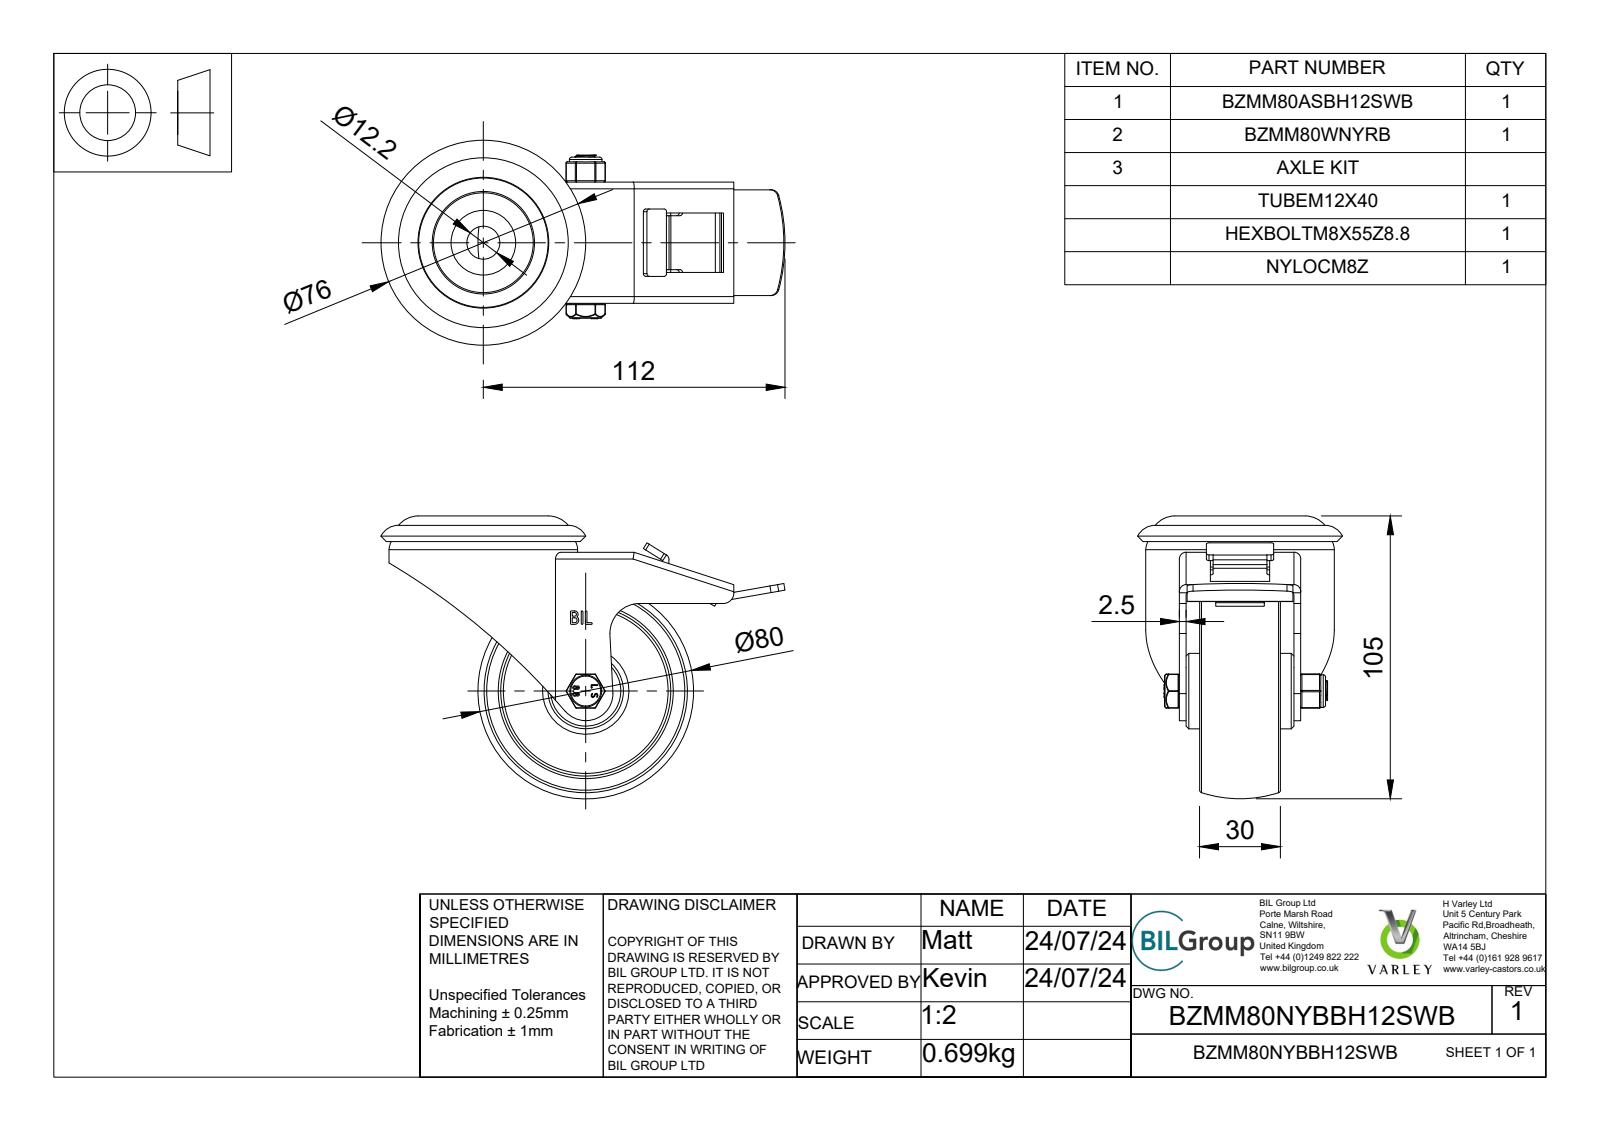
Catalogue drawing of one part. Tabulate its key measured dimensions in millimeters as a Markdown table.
| quantity | value |
| --- | --- |
| part name | BZMM80NYBBH12SWB v3; BZMM80ASBH12SWB v1; ZINC PLATED, PRESSED STEEL HEAD; ZINC PLATED, PRESSED STEEL FORKS (+8 more) |
| STEP written by | Autodesk Translation Framework v13.14.0.145 (AUTOMOTIVE_DESIGN) |
| units | millimeters |
| bodies | 19 solids, 703 faces (345 planar, 256 cylindrical, 102 other) |
| overall size | 150 × 105 × 76 |
| volume | 149 600 mm³ |
| surface area | 94 806 mm² |
| round holes (diameter × count) | 0.66 × 2, 8 × 1, 8.2 × 1, 8.4 × 1, 8.6 × 1, 12.2 × 1, 12.4 × 1, 12.5 × 1, 23 × 1, 65 × 1, 72 × 1 |
| round bosses / shafts (diameter × count) | 3.75 × 8, 70 × 1, 49.5 × 1, 38 × 1, 28 × 1, 24 × 1, 21.31 × 1, 19.5 × 1 |
| partial cylindrical surfaces (radius × count) | 0.75 × 48, 0.5 × 26, 0.25 × 12, 1 × 6, 1.25 × 6, 2 × 5, 2.5 × 5, 0.33 × 4 |
| main face-to-face distances | 2.5, 18, 22, 4, 20.5, 24.5, 42.5, 40, 13, 5 |
| hole center spacings | 3.22, 2.49 |
